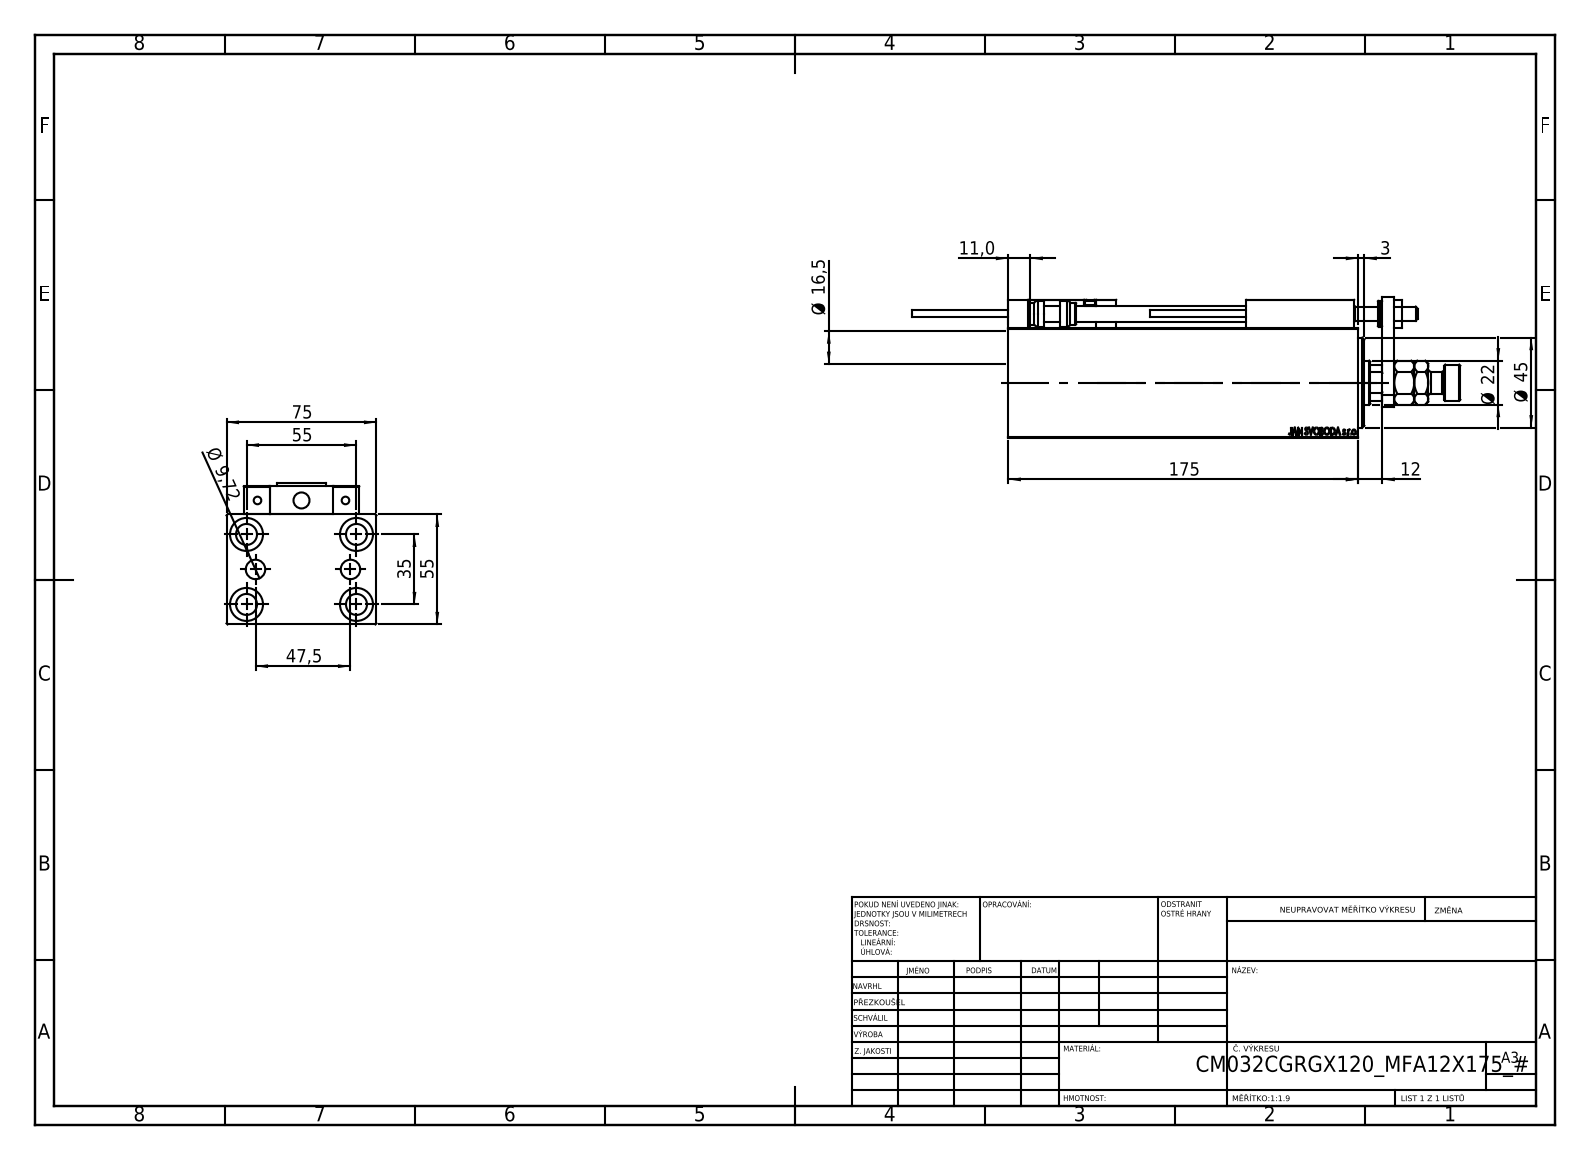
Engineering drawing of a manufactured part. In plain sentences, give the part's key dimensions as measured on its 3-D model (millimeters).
The part is named "V450CM_C_VCP; NUT_D12; Block; KONCOVKA (+8 more)". Its 3-D file was written by "SolidWorks 2019 (CONFIG_CONTROL_DESIGN)". It is 24 solids with 1324 faces: 574 planar, 184 cylindrical and 566 other. Overall it measures 274 by 75 by 70.5 millimeters. Its volume is 664 008 cubic millimeters and its surface area 145 118 square millimeters. Round holes: 5 of diameter 8, 5 of diameter 10.5, 5 of diameter 16.5, 4 of diameter 3.2, 4 of diameter 4, 2 of diameter 5, 2 of diameter 9.72, 1 of diameter 7, 1 of diameter 22, 1 of diameter 25.5, 1 of diameter 32, 1 of diameter 34. Round bosses or shafts: 2 of diameter 11, 2 of diameter 5, 2 of diameter 3.8, 1 of diameter 18, 1 of diameter 13. Partial cylindrical surfaces (rounded edges, fillets, slot ends): 30 of radius 0.3, 2 of radius 3, 1 of radius 10.5. The main face-to-face distances are 55, 75, 14, 10, 12, 7, 3, 69, 23, 18. The hole center spacings are 32.6, 11.37, 17.76, 18.07, 20, 29.59, 29.69, 32.33.
